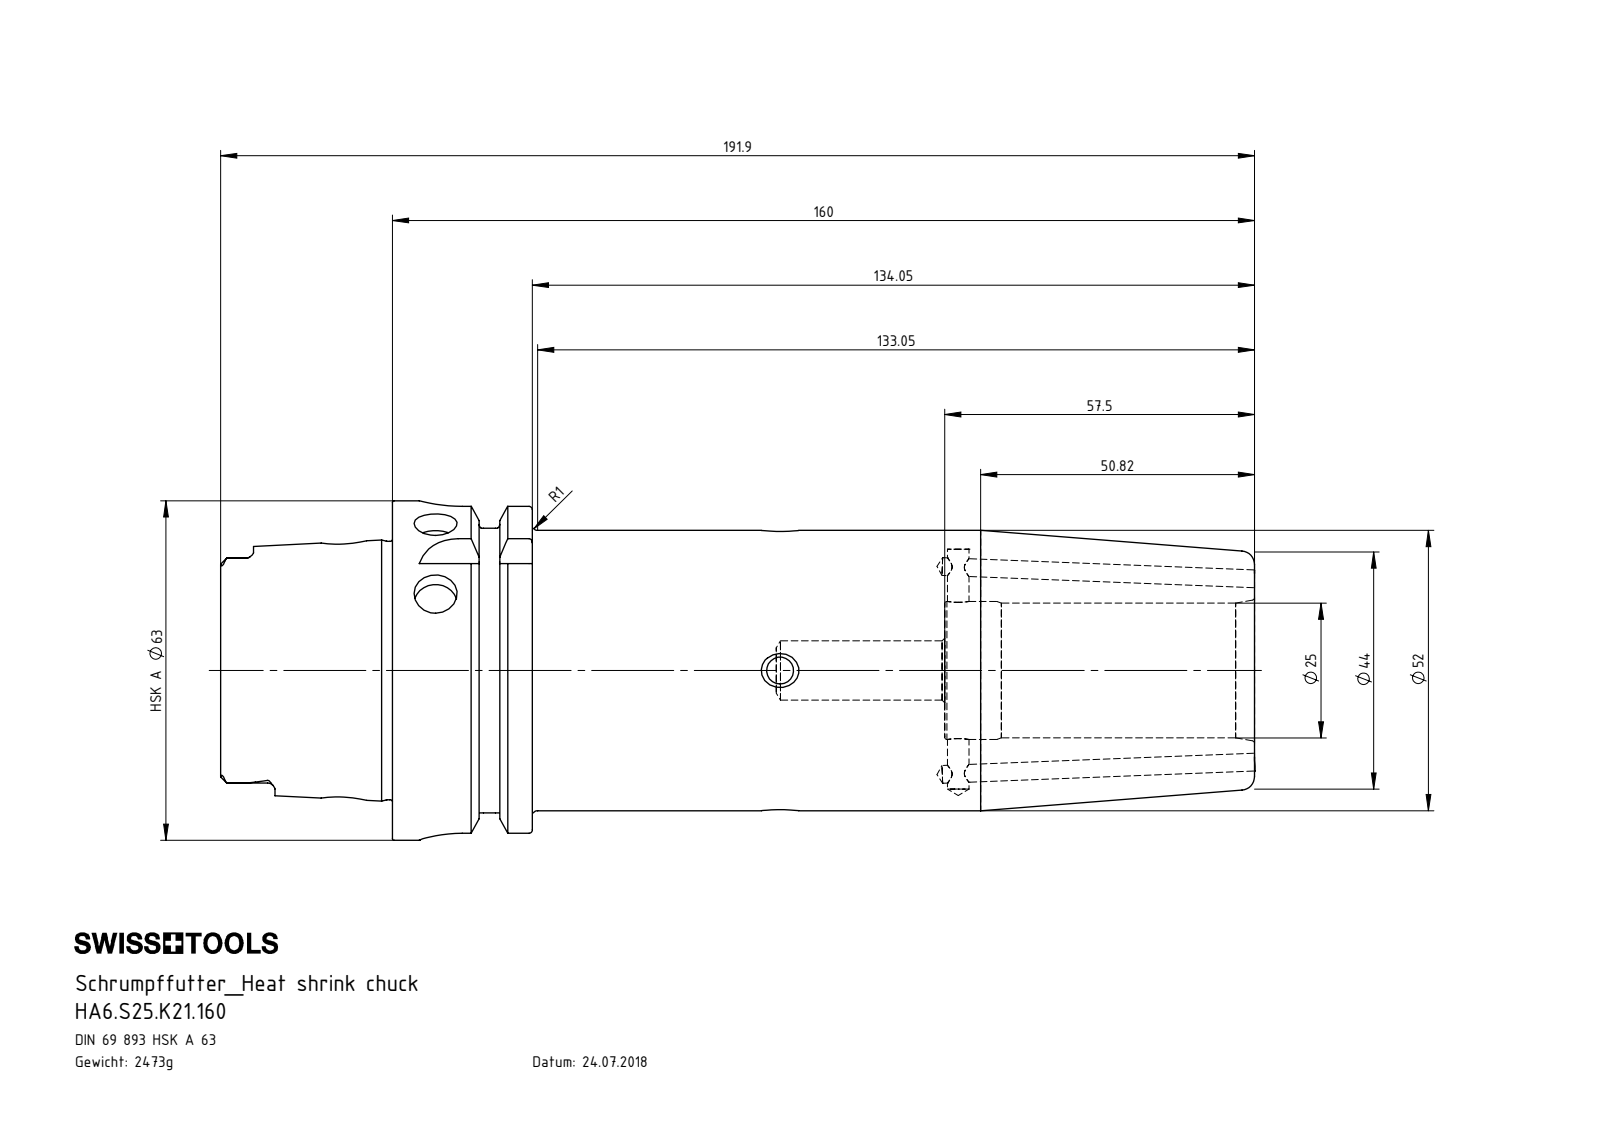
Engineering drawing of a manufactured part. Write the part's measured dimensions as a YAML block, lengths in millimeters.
part_name: "HA6-S25.K21.160_C_Fertigbearbeitung; HA6-S25.K21.160; ERU-CJ3.001.008; ERU-AN5.K01.020_A"
step_written_by: "SolidWorks 2012 (CONFIG_CONTROL_DESIGN)"
units: millimeters
bodies: {solids: 4, faces: 318, planar: 102, cylindrical: 87, other: 129}
overall_size: [192, 63, 63]
volume: 315018
surface_area: 53407
round_holes:
  - {diameter: 3.3, count: 2}
  - {diameter: 5, count: 2}
  - {diameter: 8, count: 2}
  - {diameter: 4, count: 1}
  - {diameter: 6, count: 1}
  - {diameter: 7.5, count: 1}
  - {diameter: 8.4, count: 1}
  - {diameter: 10, count: 1}
  - {diameter: 11, count: 1}
  - {diameter: 17, count: 1}
  - {diameter: 19, count: 1}
  - {diameter: 25, count: 1}
round_bosses_or_shafts:
  - {diameter: 4, count: 2}
  - {diameter: 63, count: 1}
  - {diameter: 54.95, count: 1}
  - {diameter: 52, count: 1}
  - {diameter: 47.94, count: 1}
  - {diameter: 12, count: 1}
partial_cylinders:
  - {radius: 1.4, count: 6}
  - {radius: 2.88, count: 4}
  - {radius: 8, count: 4}
face_to_face_distances: [160, 25.95, 134.05, 16, 9.95, 150.05, 102.5, 92.55, 76.55, 57.5]
hole_center_spacings: [33.05, 64.95, 80.95, 114]
